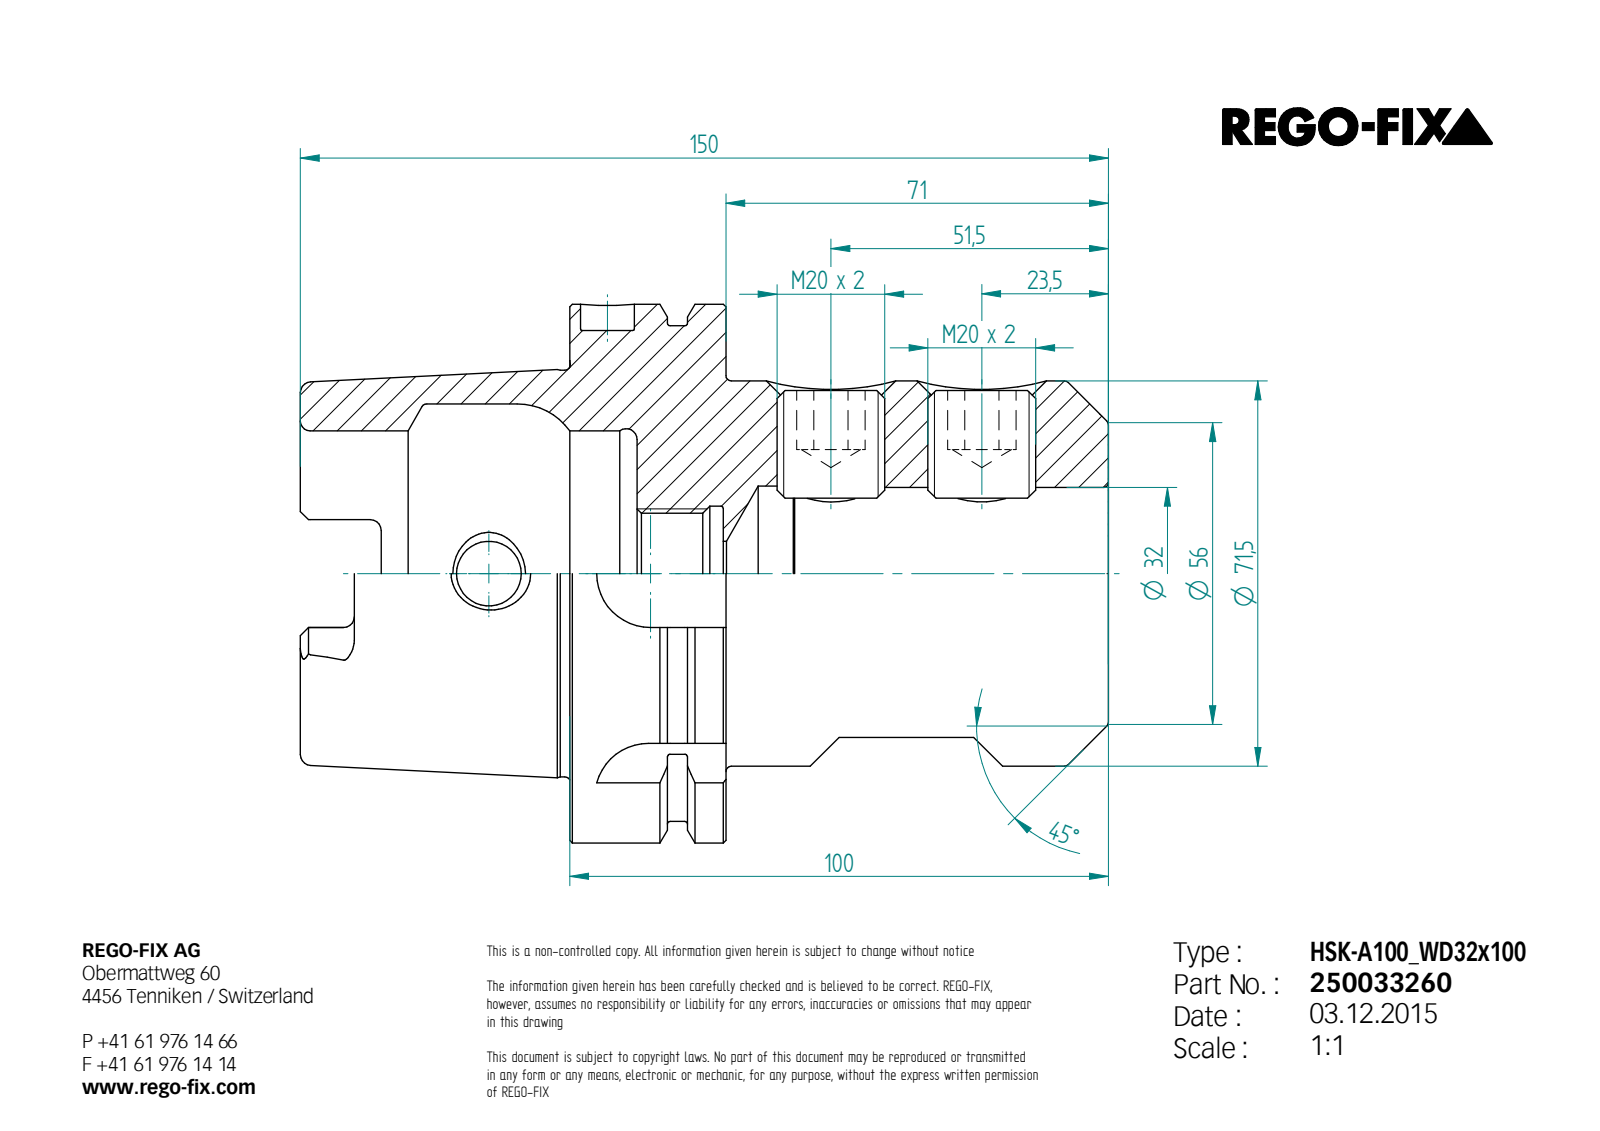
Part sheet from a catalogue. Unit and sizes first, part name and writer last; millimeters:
Units: millimetres
Overall size (bounding box): 150 × 100 × 100
Round holes (diameter × count): ⌀12 ×2, ⌀17.84 ×2, ⌀8.5 ×1, ⌀10 ×1, ⌀22.38 ×1, ⌀25 ×1, ⌀32 ×1, ⌀32.5 ×1, ⌀53 ×1, ⌀63 ×1
Round bosses / shafts (diameter × count): ⌀20 ×2, ⌀100 ×1, ⌀92 ×1, ⌀75.46 ×1, ⌀71.5 ×1
Partial cylindrical surfaces — rounded edges, fillets, slot ends (radius × count): R2 ×6, R4.88 ×4, R10 ×2, R11 ×1
Main face-to-face distances: 29, 12.5, 100, 71, 16.5, 87.5, 50, 62.5, 79, 150
Hole centre spacings: 28, 41.5, 69.5
Volume: 473 457 mm³ · Surface area: 76 325 mm²
Bodies: 3 solids, 164 faces (66 planar, 38 cylindrical, 60 other)
STEP written by: Unknown (AUTOMOTIVE_DESIGN)
